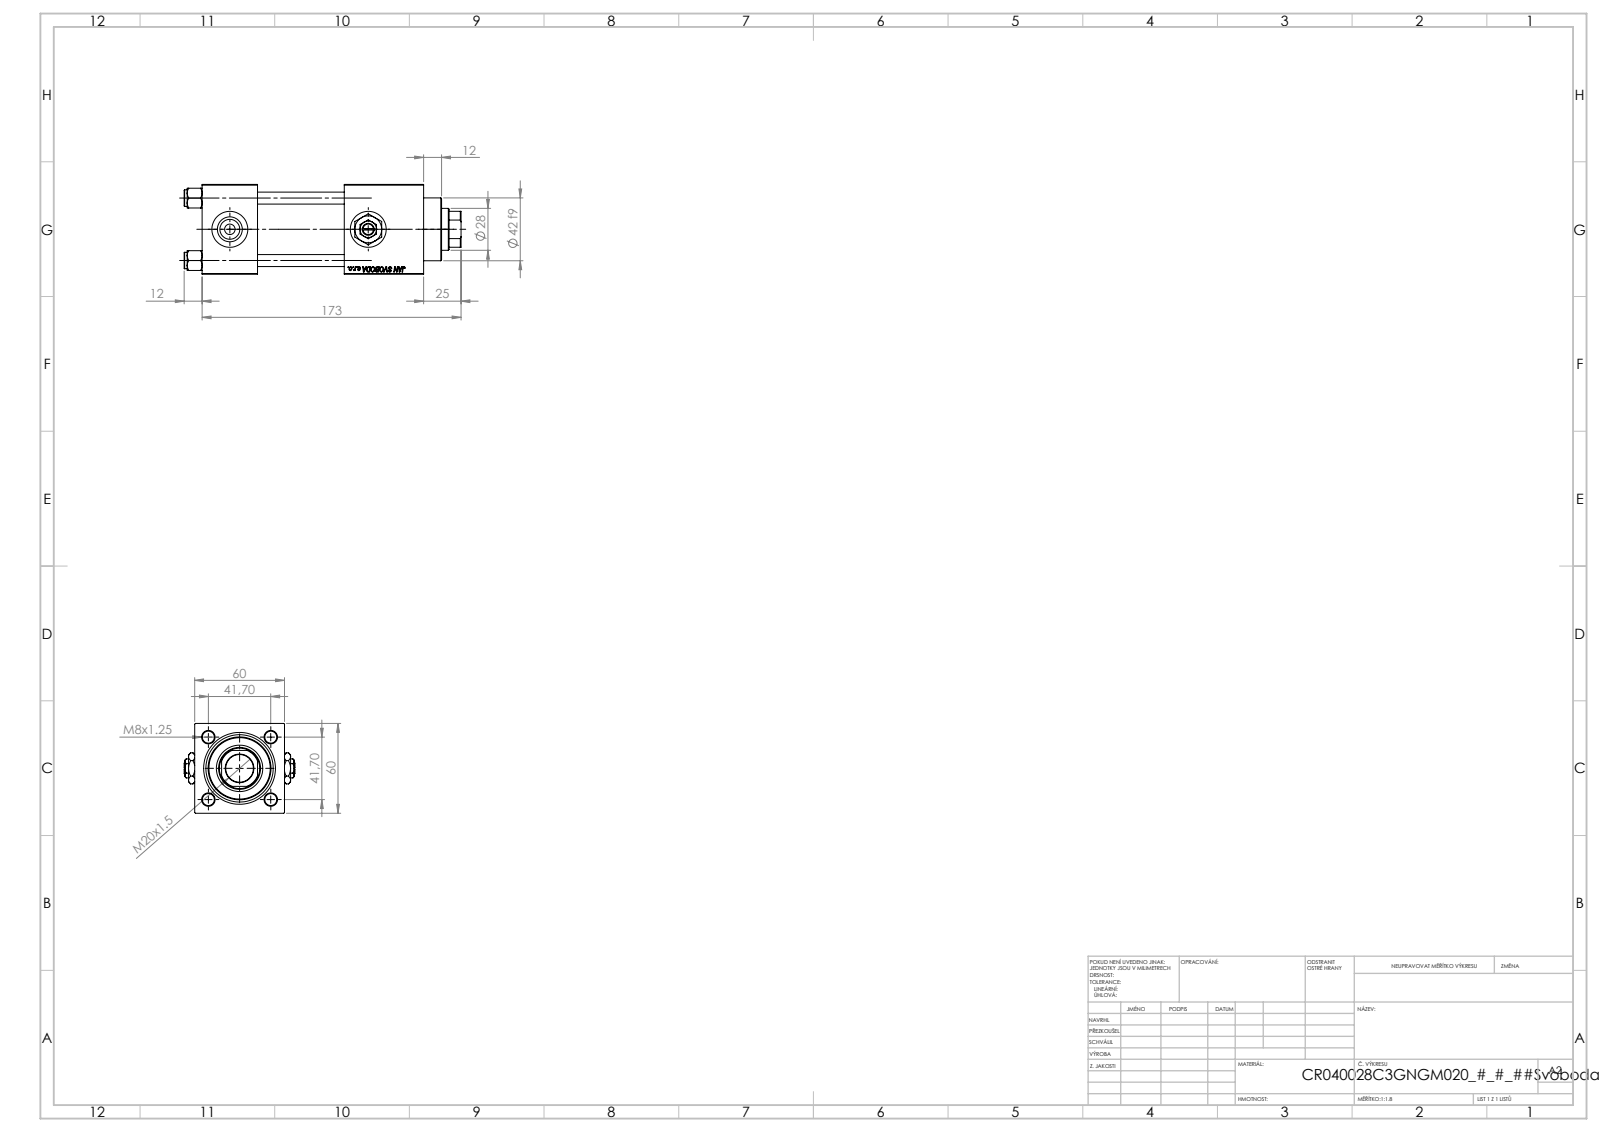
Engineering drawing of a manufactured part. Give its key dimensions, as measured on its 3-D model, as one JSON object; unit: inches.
{"part_name": "Zatka_pro_OIL_PORT; V215CR_VCP_C; V215_VC_A; NUT_M5_C (+2 more)", "step_written_by": "SolidWorks 2019 (CONFIG_CONTROL_DESIGN)", "units": "inches", "bodies": {"solids": 13, "faces": 1250, "planar": 574, "cylindrical": 98, "other": 578}, "overall_size": [7.283, 2.913, 2.362], "volume_in3": 25.69, "surface_area_in2": 177.2, "round_holes": [[0.315, 4], [0.276, 2], [0.656, 2], [0.945, 2], [0.728, 1], [1.102, 1], [1.22, 1], [1.575, 1], [1.772, 1]], "round_bosses_or_shafts": [[0.433, 4], [1.811, 1], [1.654, 1]], "partial_cylinders_radius": [[0.531, 1]], "face_to_face_distances": [2.362, 1.457, 2.283, 3.74, 2.087, 4.697, 3.24, 0.957, 5.827, 4.37], "hole_center_spacings": [1.161, 1.642, 2.322, 3.642]}
